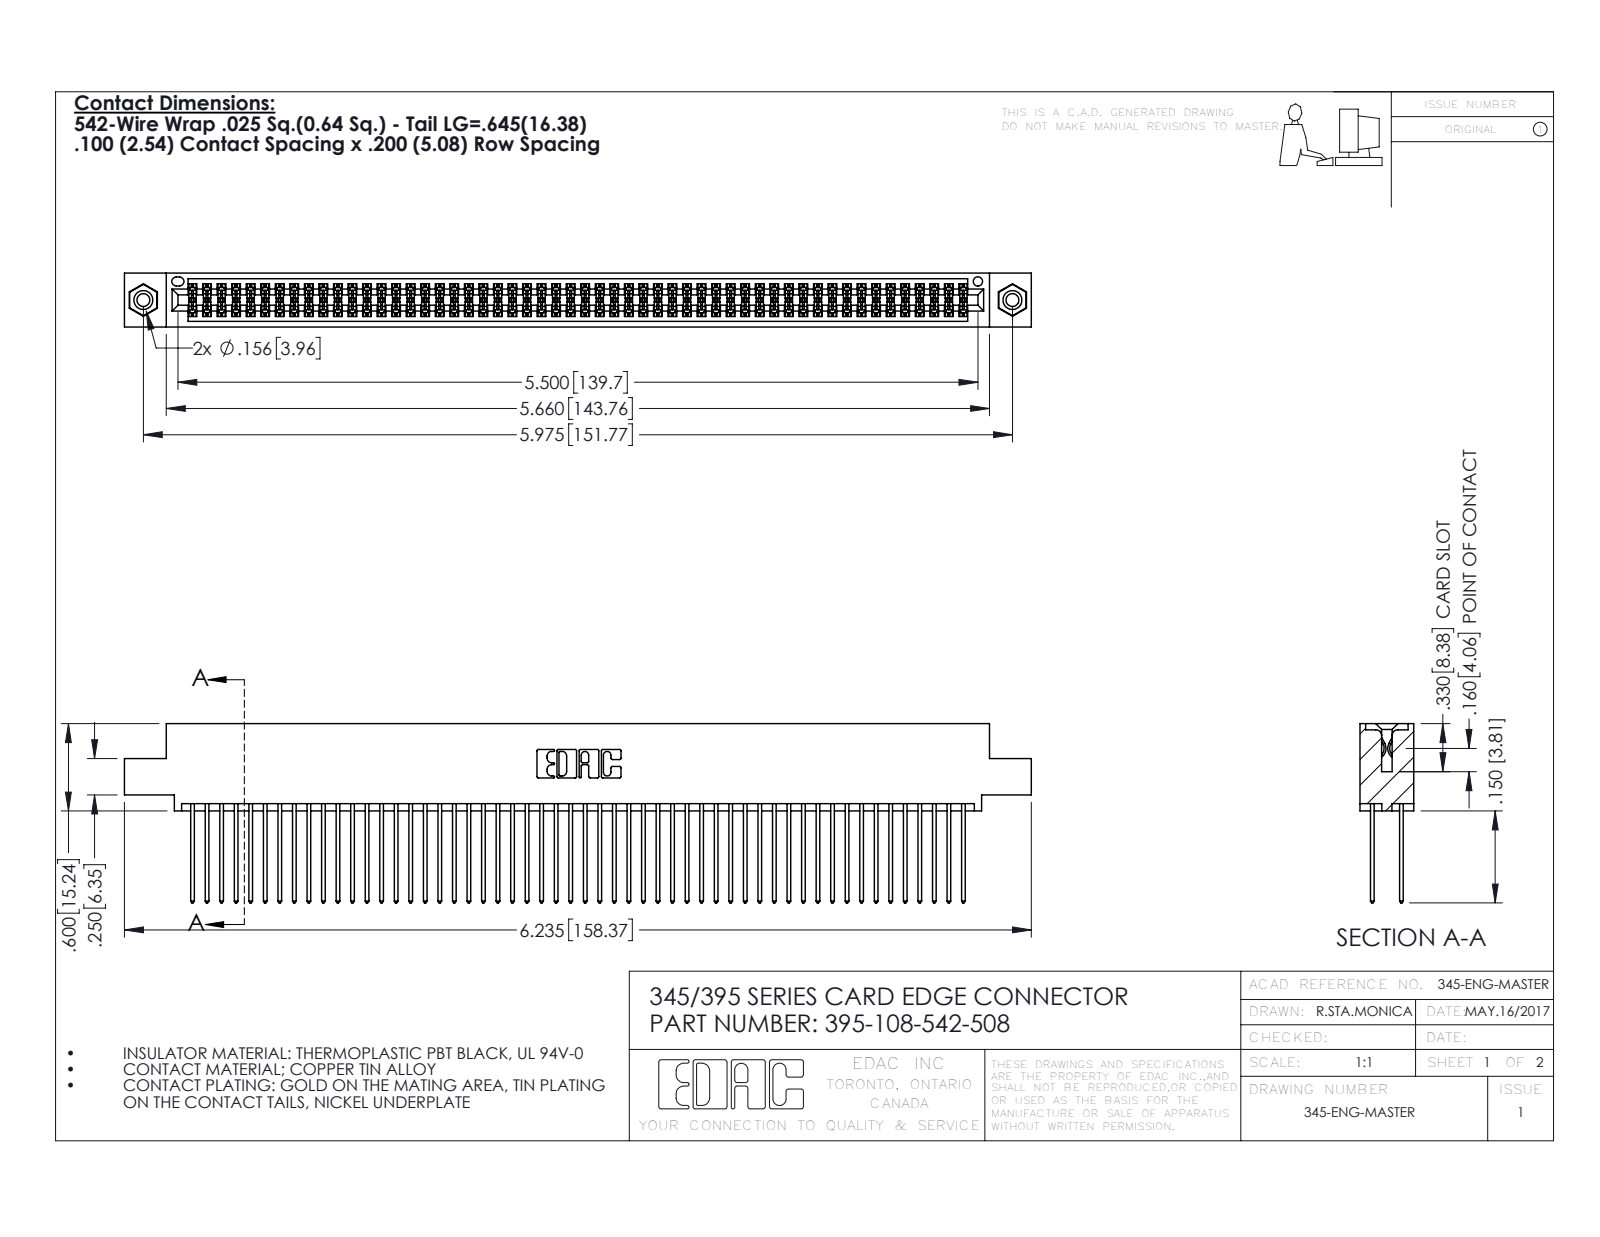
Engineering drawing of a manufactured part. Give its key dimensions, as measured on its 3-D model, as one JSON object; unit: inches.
{"part_name": "345-292-001_345-293-142; 395-108-542-508; 345 Part_0.110 Offset - 0.156 Dia-TI; 345-250-001_345-250-003-102", "step_written_by": "SolidWorks 2016 (CONFIG_CONTROL_DESIGN)", "units": "inches", "bodies": {"solids": 111, "faces": 5590, "planar": 3680, "cylindrical": 1894, "other": 16}, "overall_size": [6.235, 1.232, 0.37], "volume_in3": 0.971, "surface_area_in2": 40.64, "round_holes": [[0.089, 2], [0.125, 2], [0.156, 2], [0.064, 1]], "round_bosses_or_shafts": [[0.155, 2]], "partial_cylinders_radius": [[0.006, 162], [0.01, 108], [0.01, 22], [0.007, 6], [0.031, 6], [0.026, 3], [0.014, 2], [0.019, 2]], "face_to_face_distances": [0.072, 0.298, 0.2, 0.098, 0.272, 0.025, 0.225, 0.37, 0.175, 0.149], "hole_center_spacings": [0.27, 5.739, 5.975]}
